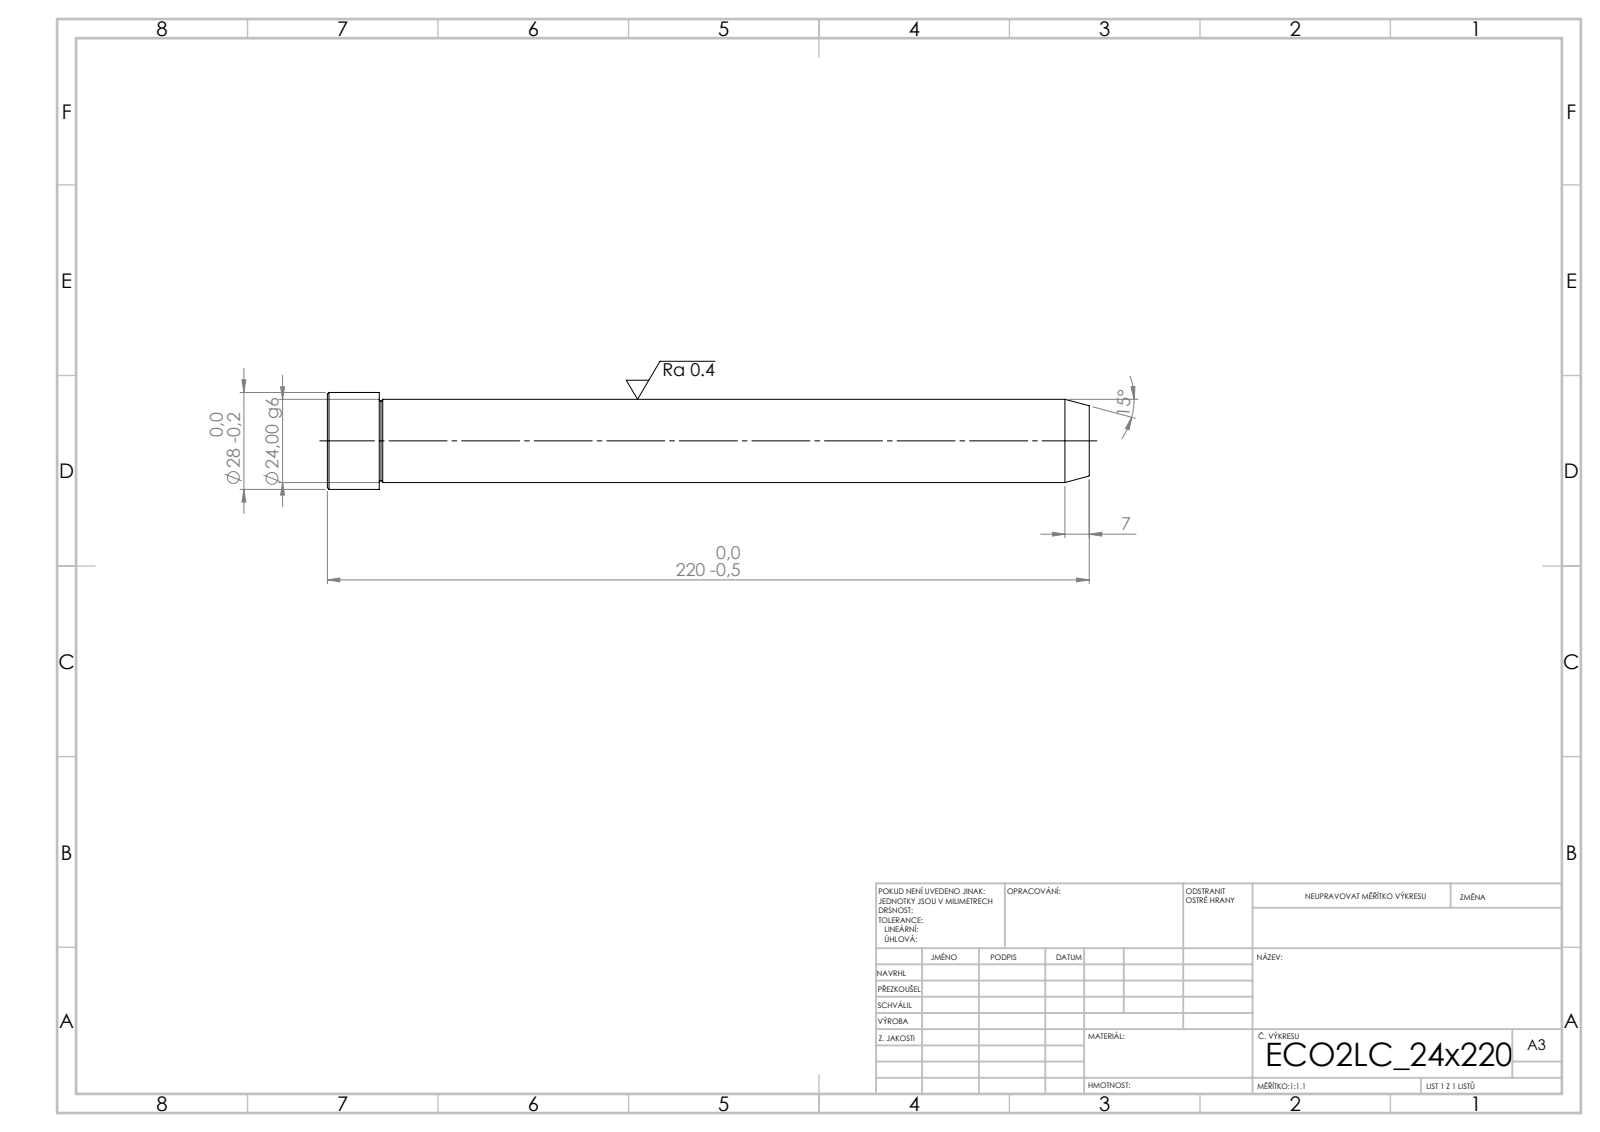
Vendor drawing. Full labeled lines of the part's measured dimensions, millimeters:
STEP written by: SolidWorks 2019 (CONFIG_CONTROL_DESIGN)
Units: millimetres
Bodies: 1 solid, 15 faces (3 planar, 4 cylindrical, 8 other)
Overall size (bounding box): 220 × 28 × 28
Volume: 101 467 mm³ · Surface area: 17 867 mm²
Round bosses / shafts (diameter × count): ⌀28 ×1, ⌀24 ×1
Main face-to-face distances: 220, 205, 15
